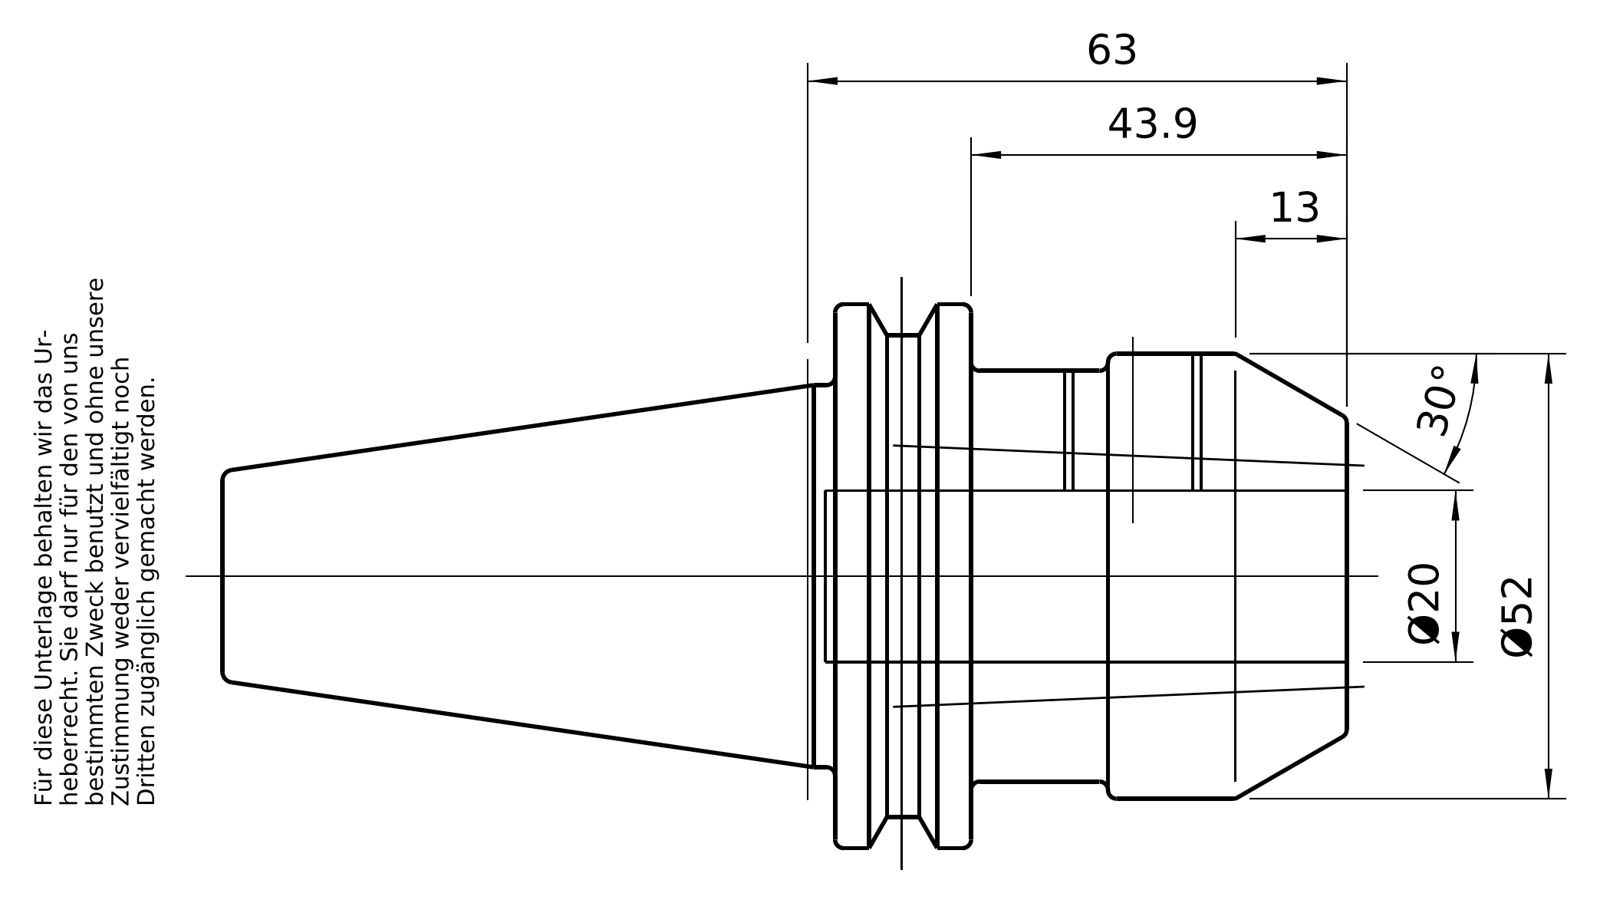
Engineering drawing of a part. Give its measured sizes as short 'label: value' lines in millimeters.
name: 40-300-20
written by: PRO/ENGINEER BY PARAMETRIC TECHNOLOGY CORPORATION, 2010430 (CONFIG_CONTROL_DESIGN)
unit: mm
bodies: 1 solid, 104 faces (23 planar, 30 cylindrical, 51 other)
size: 131.25 × 63.52 × 61.42
volume: 165 519 mm³; area: 31 304 mm²
holes: 1× ⌀13.84, 1× ⌀14, 1× ⌀16, 1× ⌀17.01, 1× ⌀17.5, 1× ⌀20
bosses: 1× ⌀52, 1× ⌀48, 1× ⌀43.75, 1× ⌀16.01
rounds: 1× R1.35, 1× R28, 1× R31.76
face distances: 15.85, 59.8, 43.95, 16.15, 60.1, 47.4, 16.2, 71.15, 71.45, 87.3
